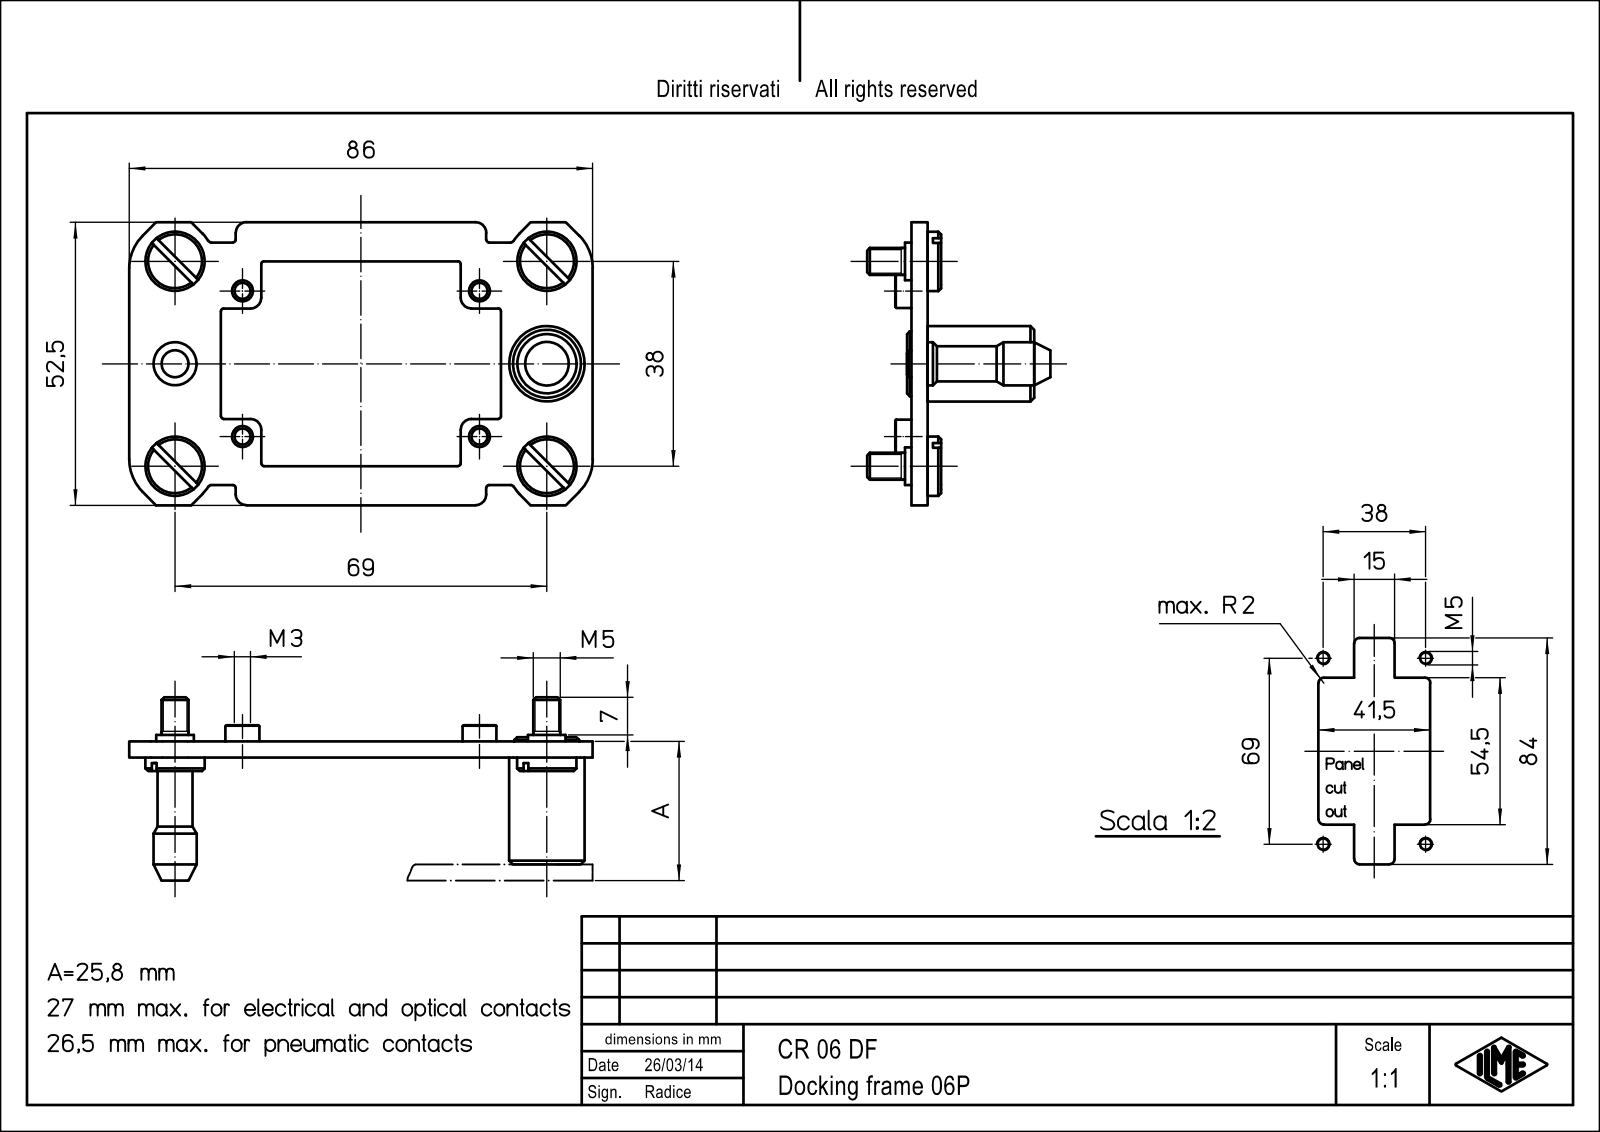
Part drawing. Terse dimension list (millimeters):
name: CR_06_DF
written by: Creo Elements/Direct Modeling 18.0B 02-Dec-2011 (C) Parametric Technology GmbH (AUTOMOTIVE_DESIGN)
unit: mm
bodies: 1 solid, 684 faces (532 planar, 112 cylindrical, 40 other)
size: 86 × 52.5 × 34.2
volume: 11 667 mm³; area: 10 856 mm²
holes: 4× ⌀2.55, 4× ⌀4.25, 4× ⌀9, 1× ⌀4.05, 1× ⌀8.15, 1× ⌀9.6, 1× ⌀12.05
bosses: 4× ⌀11, 4× ⌀7, 4× ⌀5, 1× ⌀14, 1× ⌀12, 1× ⌀8, 1× ⌀6.5, 1× ⌀4
rounds: 16× R0.5, 8× R2, 4× R2.55, 4× R7.25, 4× R8.5
face distances: 3, 5.5, 2.5, 7.25, 45.25, 52.5, 17, 69, 38, 86
hole spacings: 13.66, 18.4, 19, 34.82, 56.77, 58.09, 65.18, 71.57
